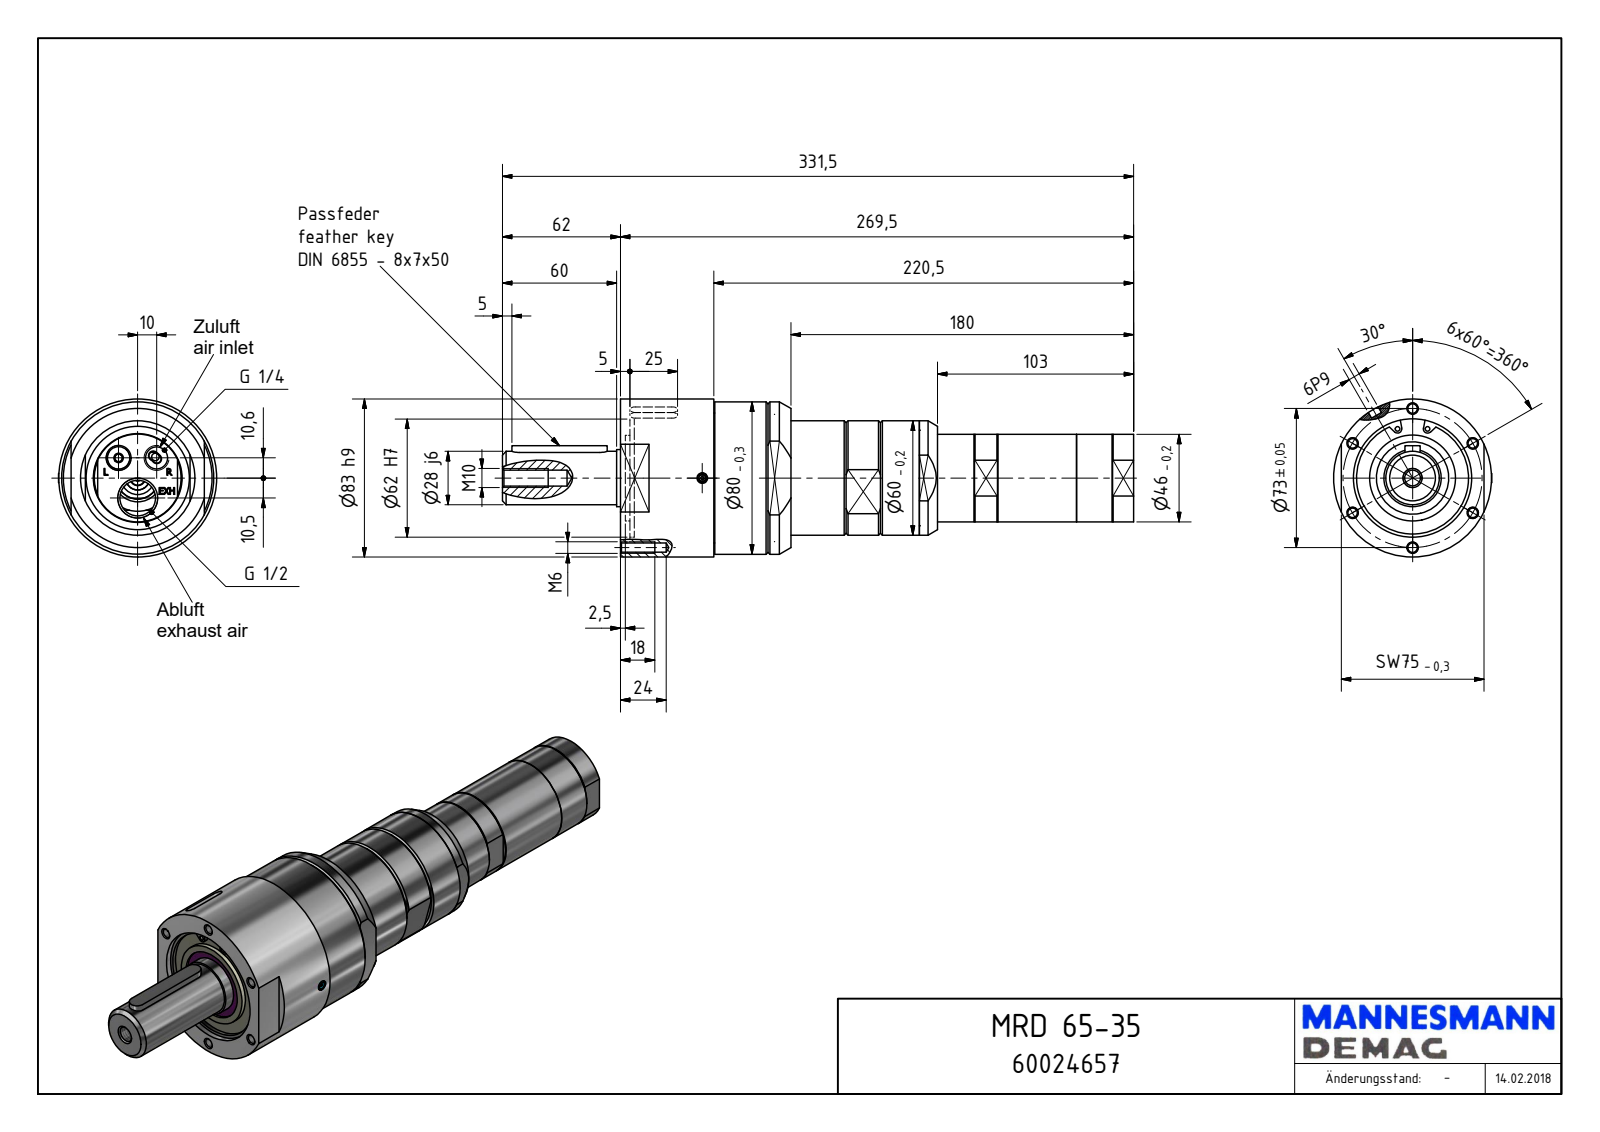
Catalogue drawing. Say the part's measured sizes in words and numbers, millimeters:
The part is named "MRD 65-35_60024657". Its 3-D file was written by "Autodesk Inventor 2018 (AUTOMOTIVE_DESIGN)". It is 1 solid with 261 faces: 137 planar, 64 cylindrical and 60 other. Overall it measures 331.5 by 83 by 83 millimeters. Its volume is 871 595 cubic millimeters and its surface area 79 653 square millimeters. Round holes: 6 of diameter 4.92, 3 of diameter 1.55, 3 of diameter 4, 2 of diameter 5.5, 1 of diameter 8.38, 1 of diameter 11.45, 1 of diameter 18.63, 1 of diameter 46.5, 1 of diameter 62, 1 of diameter 68.38. Round bosses or shafts: 2 of diameter 5, 2 of diameter 3.6, 1 of diameter 83, 1 of diameter 80, 1 of diameter 68.18, 1 of diameter 60, 1 of diameter 53.14, 1 of diameter 46. Partial cylindrical surfaces (rounded edges, fillets, slot ends): 2 of radius 3, 2 of radius 4, 2 of radius 5, 1 of radius 5.72, 1 of radius 18.31, 1 of radius 19, 1 of radius 25.41, 1 of radius 32.5. The main face-to-face distances are 1.31, 49, 47.69, 89.5, 88.19, 40.5, 49.5, 0.5, 48.19, 40. The hole center spacings are 36.5, 63.22, 73, 14.57, 22.92, 23.35, 27.76, 32.55.
